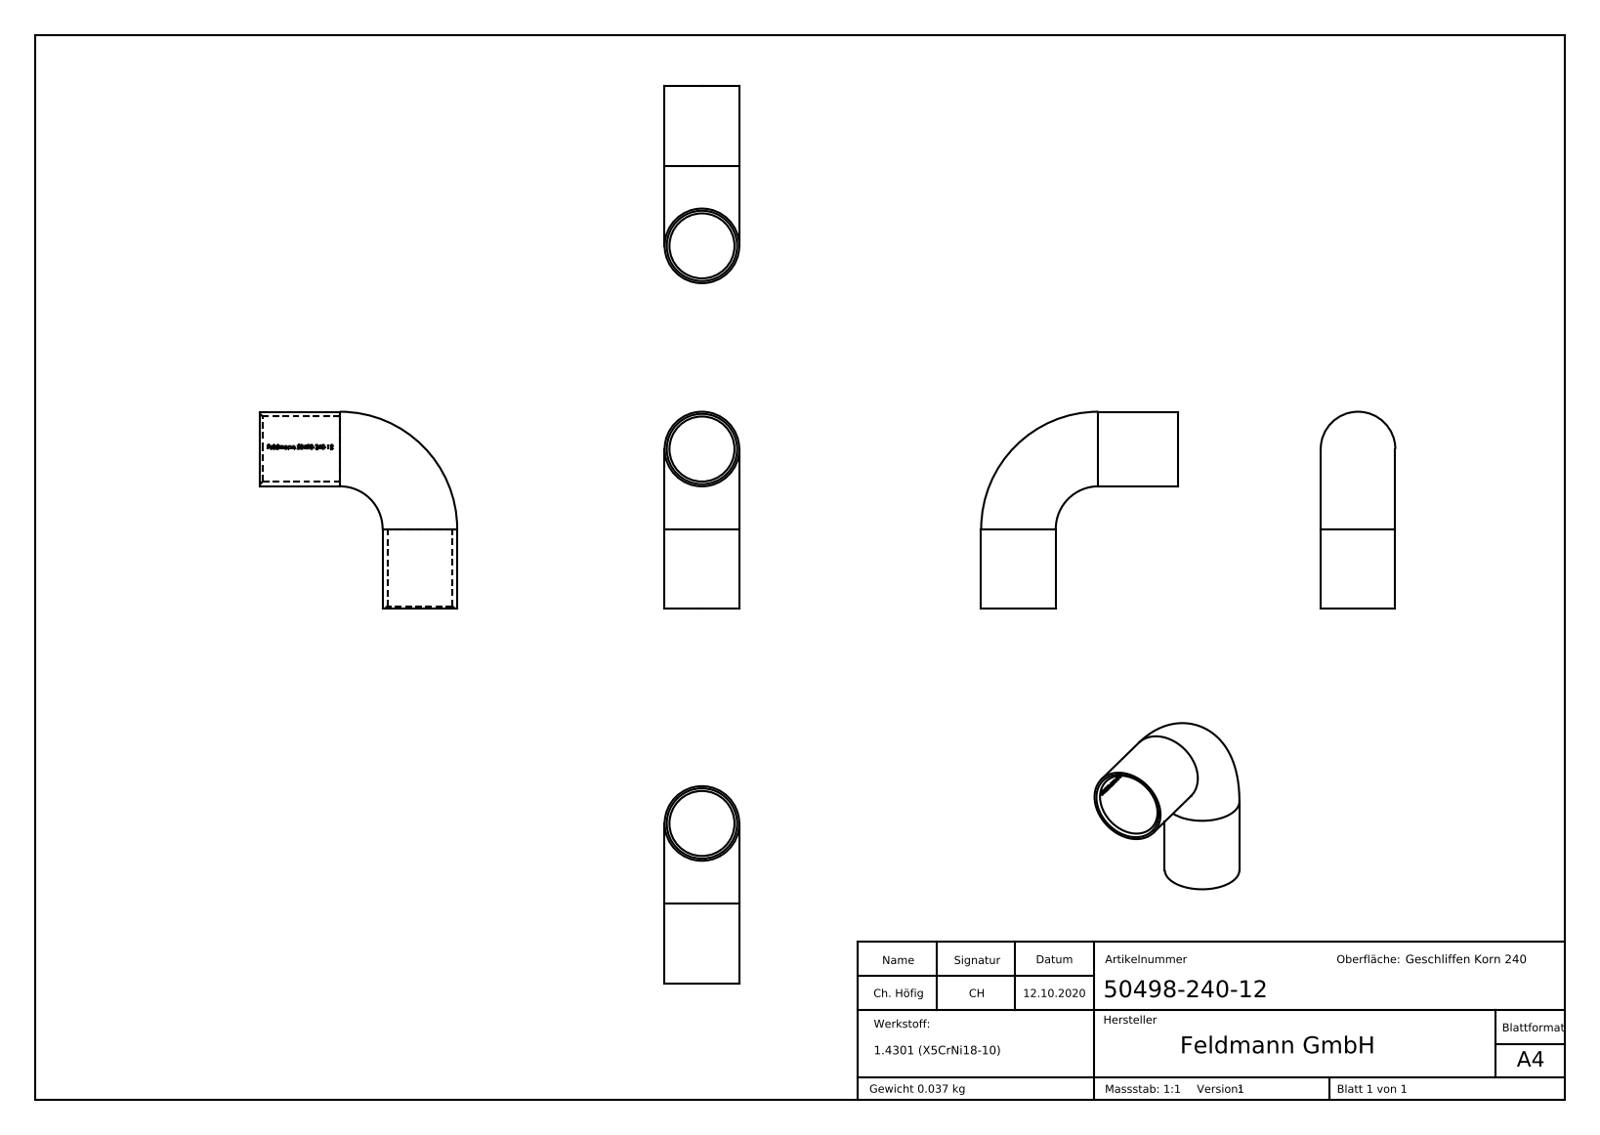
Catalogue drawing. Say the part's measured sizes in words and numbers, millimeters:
The part is named "50498-240-12". Its 3-D file was written by "SolidWorks 2018 (CONFIG_CONTROL_DESIGN)". It is 1 solid with 275 faces: 119 planar, 38 cylindrical and 118 other. Overall it measures 37 by 37 by 14 millimeters. Its volume is 4 728 cubic millimeters and its surface area 3 798 square millimeters. Round holes: 2 of diameter 12.2. Round bosses or shafts: 2 of diameter 14. Partial cylindrical surfaces (rounded edges, fillets, slot ends): 1 of radius 6.2. The main face-to-face distances are 15, 30, 11.44, 2.2, 0.53, 10.23, 1.78, 0.71, 1.21, 0.44.
